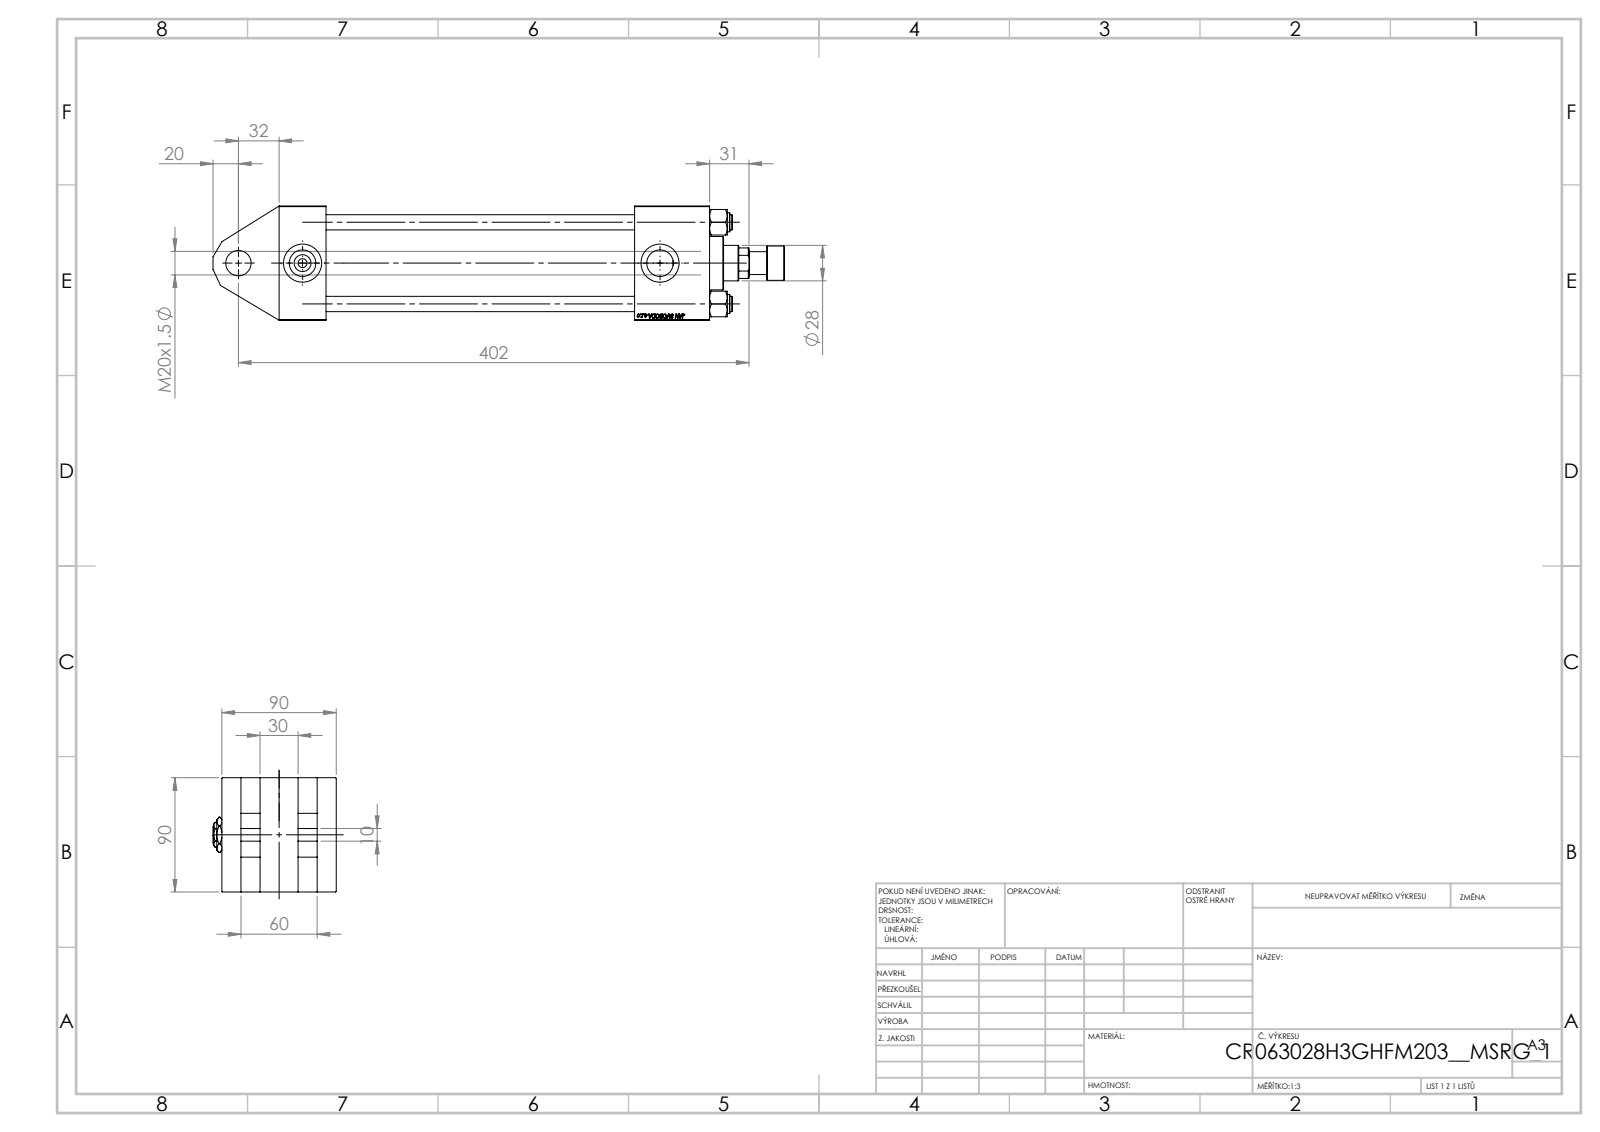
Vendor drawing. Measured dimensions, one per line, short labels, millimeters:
name: NUT_M5_H; V215CR_TYCINKA_H; Zatka_pro_OIL_PORT; V215CR_H_Body (+3 more)
written by: SolidWorks 2019 (CONFIG_CONTROL_DESIGN)
unit: mm
bodies: 14 solids, 1244 faces (570 planar, 98 cylindrical, 576 other)
size: 450 × 97 × 90
volume: 1 354 000 mm³; area: 324 800 mm²
holes: 4× ⌀12, 2× ⌀7, 2× ⌀20.96, 2× ⌀30, 1× ⌀18.5, 1× ⌀20, 1× ⌀28, 1× ⌀31, 1× ⌀50, 1× ⌀60, 1× ⌀63
bosses: 4× ⌀15, 1× ⌀69, 1× ⌀42, 1× ⌀27, 1× ⌀18
face distances: 90, 15, 60, 30, 302, 45, 37, 59, 75, 339
hole spacings: 45.47, 64.3, 90.93, 50.5, 281.5, 332
